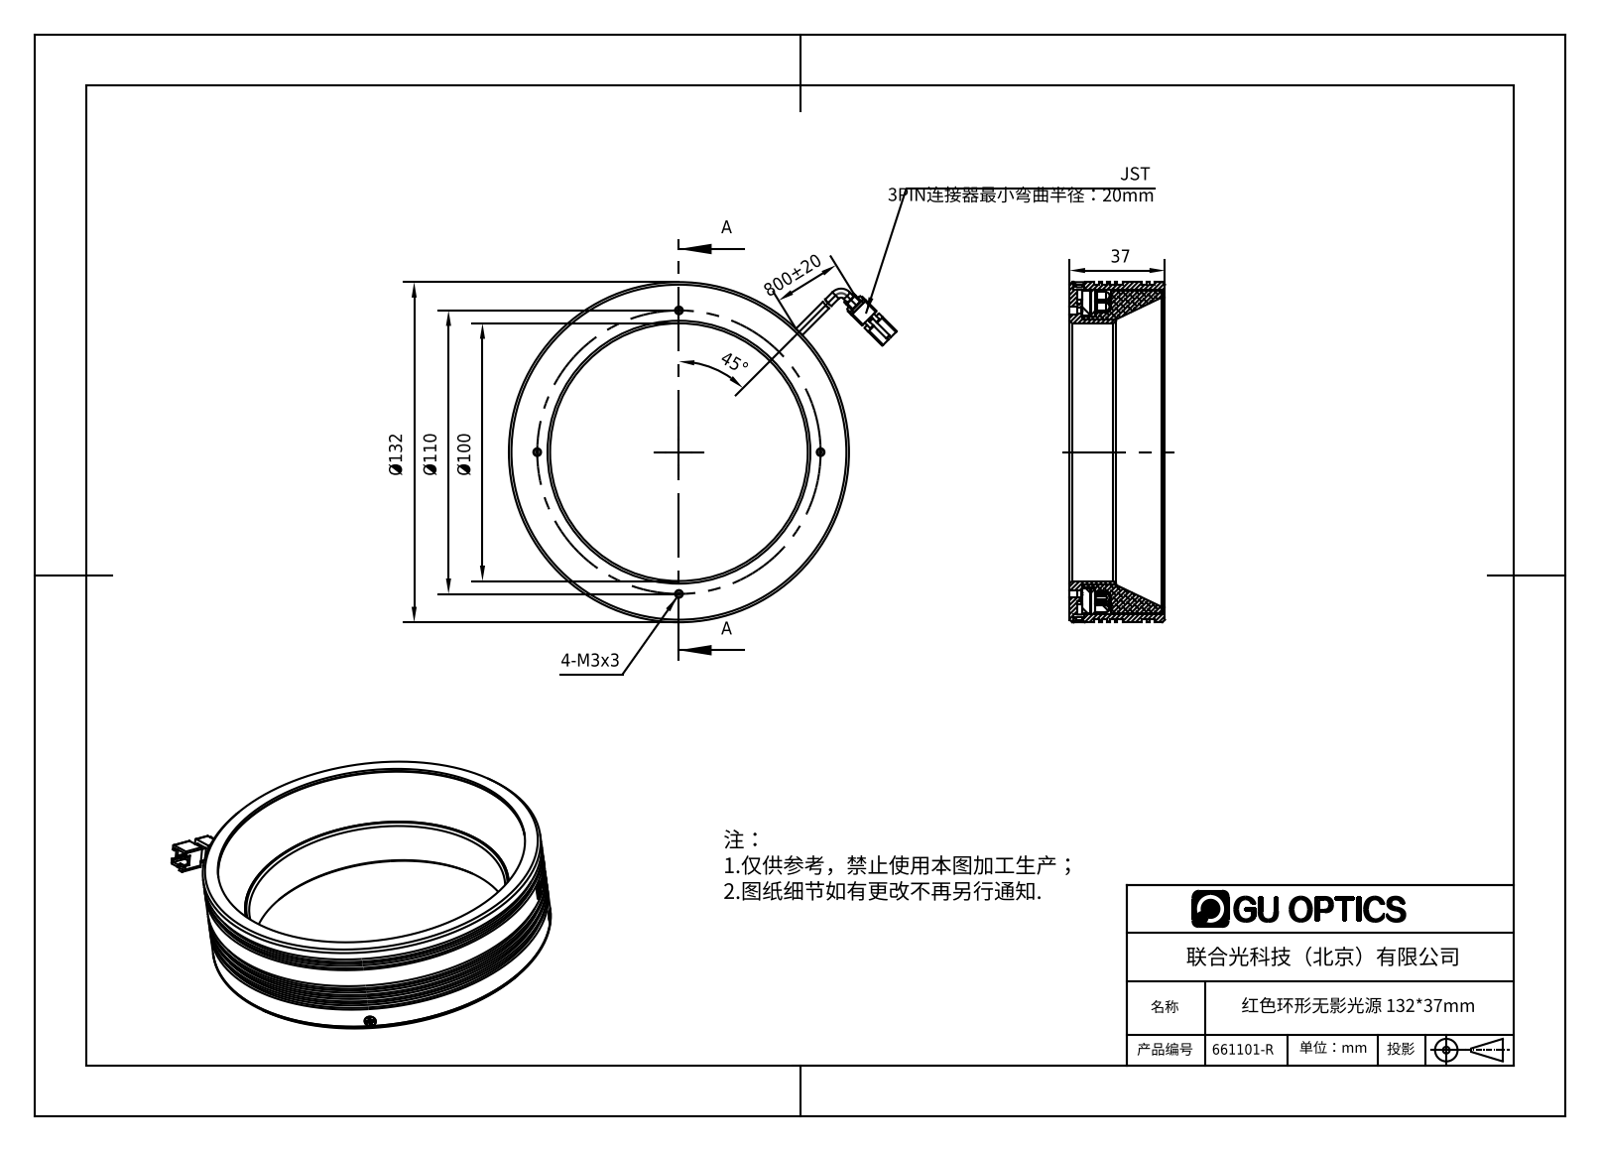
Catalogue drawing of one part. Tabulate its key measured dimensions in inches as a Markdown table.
| quantity | value |
| --- | --- |
| part name | 661101-R |
| STEP written by | SolidWorks 2016 (AUTOMOTIVE_DESIGN) |
| units | inches |
| bodies | 176 solids, 1569 faces (485 planar, 853 cylindrical, 231 other) |
| overall size | 5.926 × 5.197 × 1.457 |
| volume | 9.115 in³ |
| surface area | 186.8 in² |
| round holes (diameter × count) | 0.098 × 4, 0.118 × 4, 0.063 × 2, 0.079 × 2, 0.094 × 2, 0.138 × 1, 3.937 × 1, 4.055 × 1, 4.15 × 1, 4.173 × 1, 4.724 × 1, 5.039 × 1 |
| round bosses / shafts (diameter × count) | 0.157 × 165, 0.118 × 165, 0.138 × 2, 5.197 × 1, 5.102 × 1, 4.961 × 1, 4.953 × 1, 4.921 × 1 |
| partial cylindrical surfaces (radius × count) | 0.008 × 48, 0.02 × 12, 0.039 × 4, 0.236 × 1 |
| main face-to-face distances | 0.197, 0.315, 0.118, 0.079, 0.394, 0.236, 0.039, 0.063, 0.134, 0.331 |
| hole center spacings | 2.165, 3.062, 4.331 |
